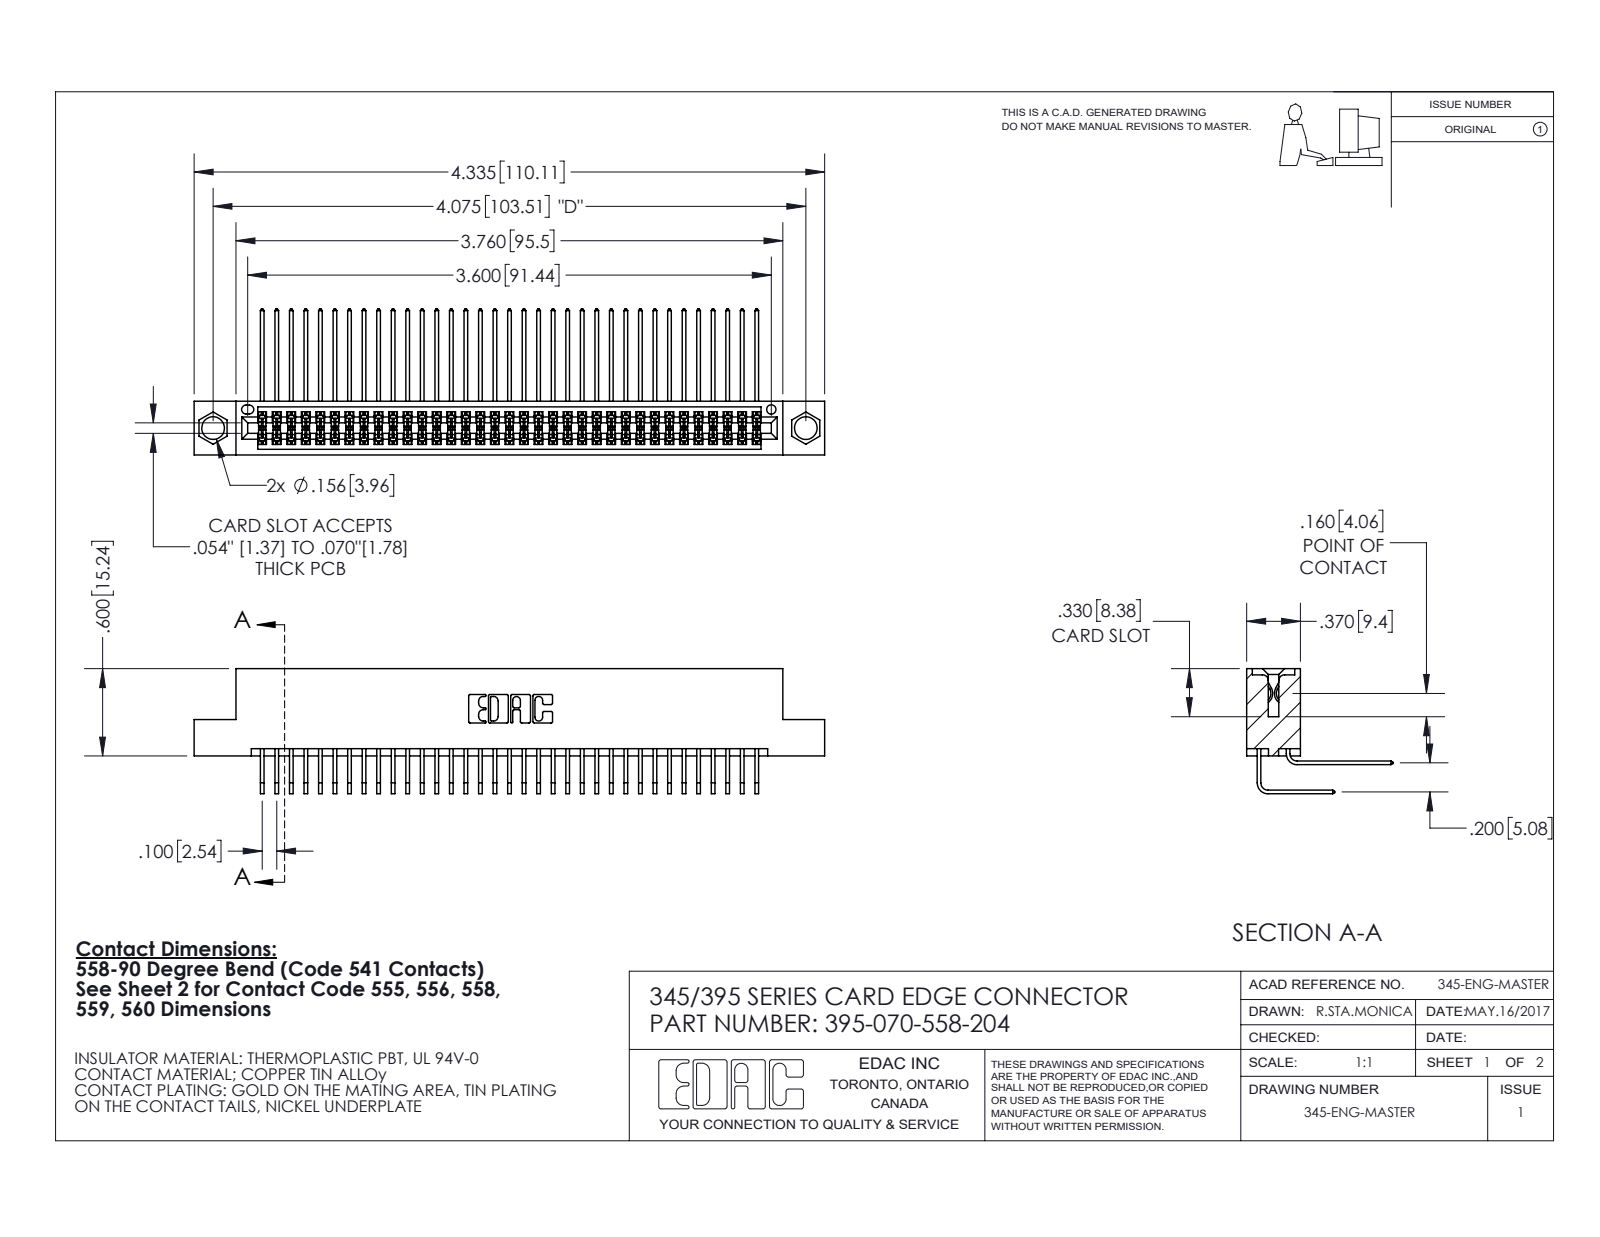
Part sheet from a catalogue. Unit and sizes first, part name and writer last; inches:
Units: inches
Overall size (bounding box): 4.335 × 1.005 × 0.859
Round holes (diameter × count): ⌀0.156 ×2, ⌀0.064 ×1
Partial cylindrical surfaces — rounded edges, fillets, slot ends (radius × count): R0.006 ×105, R0.01 ×22, R0.007 ×6, R0.031 ×6, R0.026 ×3, R0.014 ×2, R0.019 ×2, R0.022 ×2
Main face-to-face distances: 0.072, 0.298, 0.2, 0.37, 0.098, 0.272, 0.025, 0.225, 0.025, 0.175
Hole centre spacings: 0.27, 3.839, 4.075
Volume: 0.667 in³ · Surface area: 27.54 in²
Bodies: 71 solids, 3780 faces (2544 planar, 1236 cylindrical, 0 other)
Part name (STEP PRODUCT): 345-292-001_558 Tail - 2; 345 Part_Flush Mounting Lugs - 0.156 Dia-TI; 395-070-558-204; 345-292-001_558 559 Tail - 1
STEP written by: SolidWorks 2020 (CONFIG_CONTROL_DESIGN)
